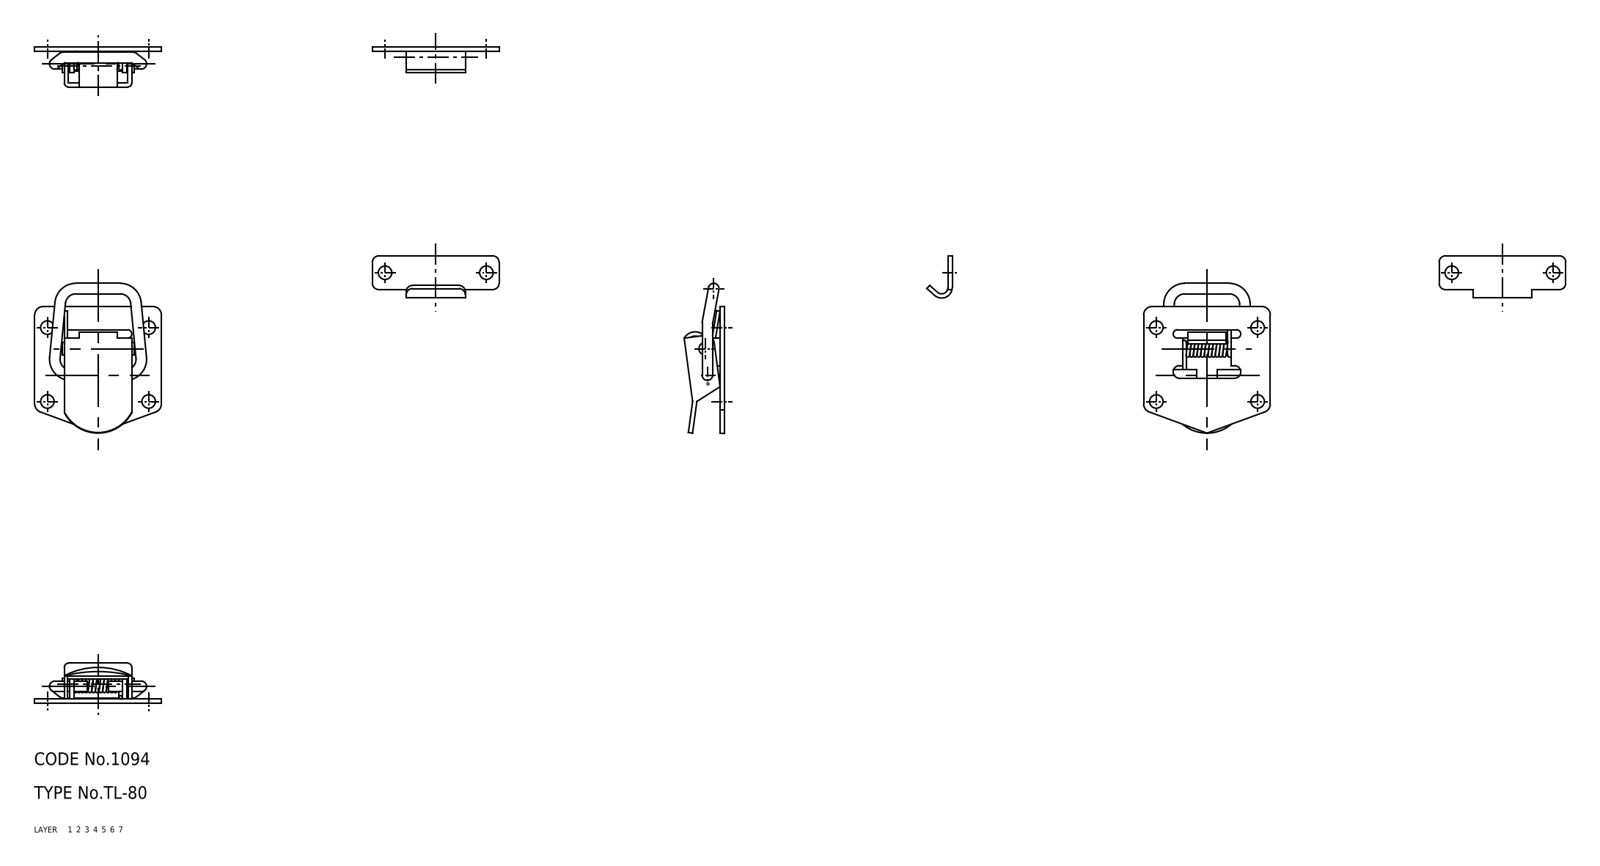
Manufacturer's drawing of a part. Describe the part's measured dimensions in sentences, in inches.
The part is named "spring; shaft; lever; keeper (+3 more)". Its 3-D file was written by "CADfix (AUTOMOTIVE_DESIGN)". It is 6 solids with 169 faces: 0 planar, 0 cylindrical and 169 other. Overall it measures 1.654 by 1.181 by 0.374 inches. Its volume is 0.123 cubic inches and its surface area 7.065 square inches.
